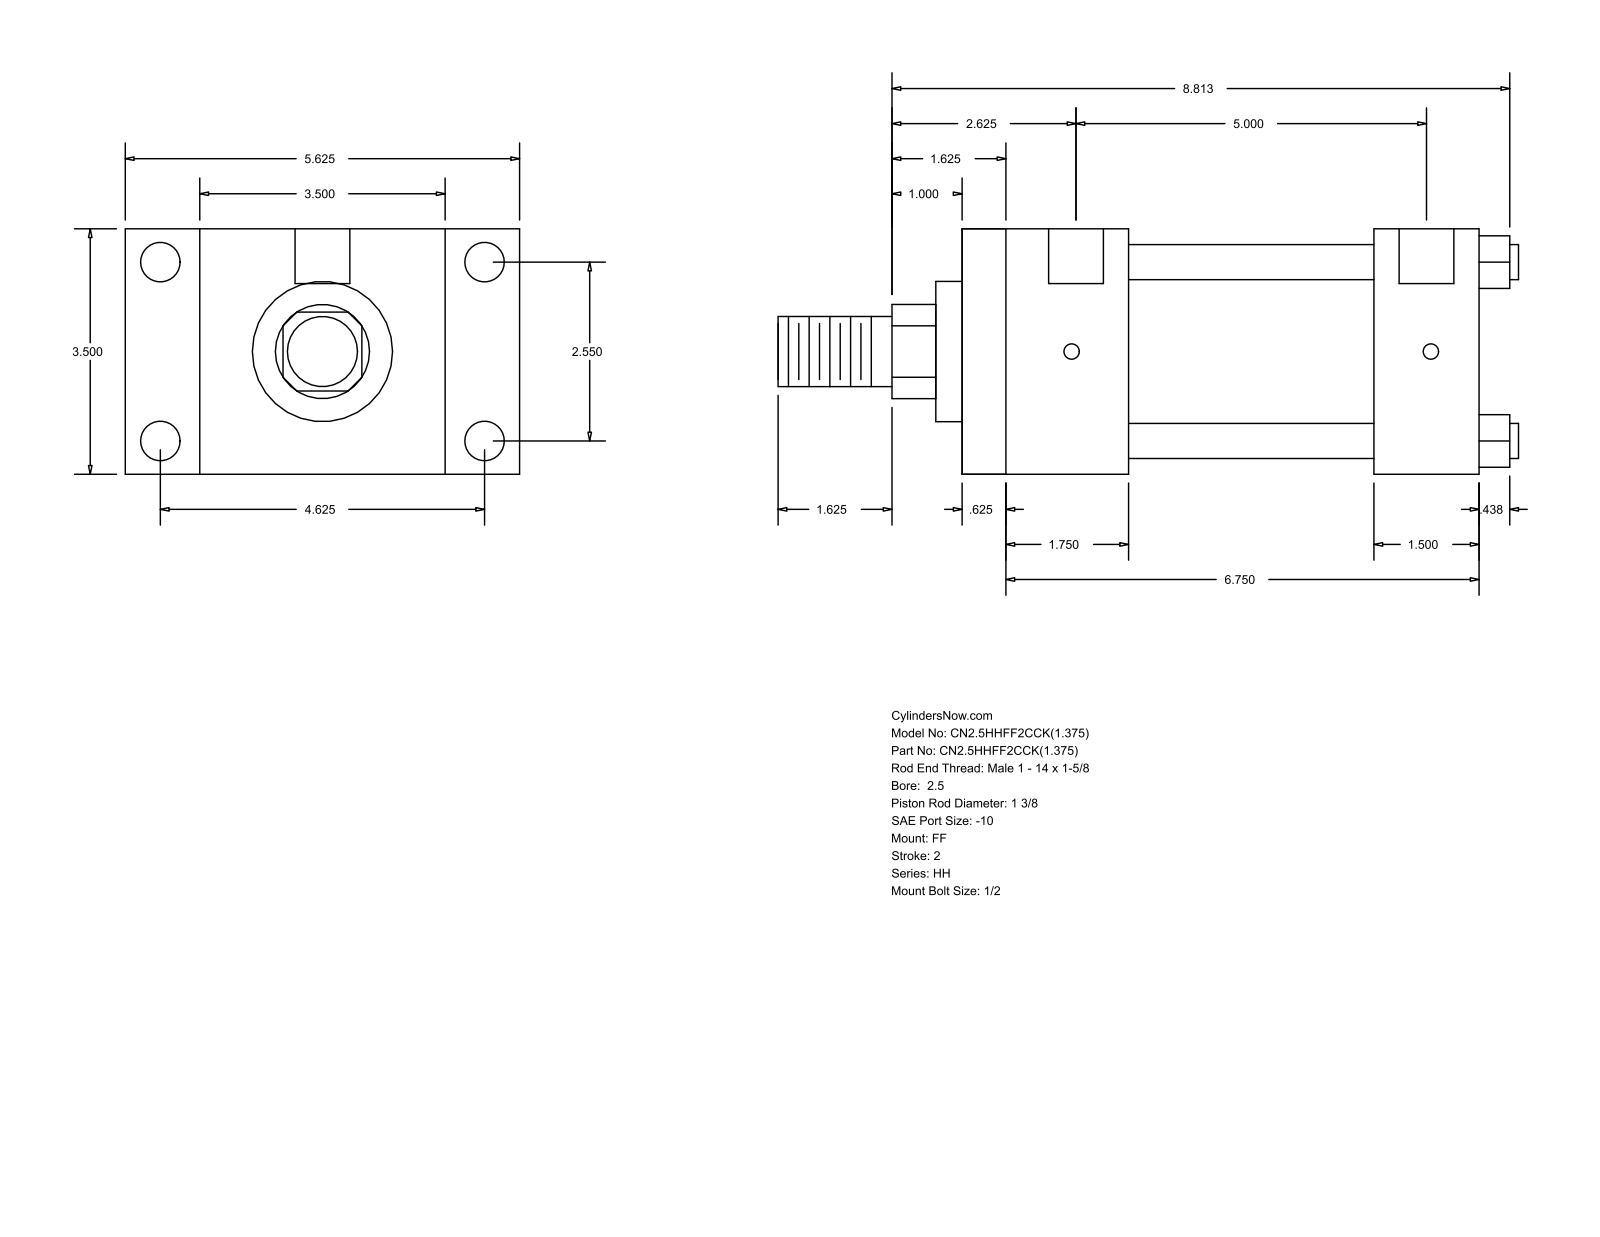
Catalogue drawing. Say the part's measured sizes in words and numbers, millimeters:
The part is named "HH_FF__0250_1.375". Its 3-D file was written by "GSSL Pune (CONFIG_CONTROL_DESIGN)". It is 0 solids with 92 faces: 64 planar, 28 cylindrical and 0 other. Overall it measures 268.29 by 142.88 by 88.9 millimeters. Round holes: 4 of diameter 5.56, 4 of diameter 14.3, 2 of diameter 19.84. Round bosses or shafts: 4 of diameter 12.7, 1 of diameter 73.03, 1 of diameter 50.8, 1 of diameter 34.92, 1 of diameter 25.4. Partial cylindrical surfaces (rounded edges, fillets, slot ends): 1 of radius 17.06. The main face-to-face distances are 88.9, 187.32, 15.87, 171.45, 60.32, 44.45, 127, 149.22, 133.35, 38.1. The hole center spacings are 1.58, 64.76, 117.48, 128.59, 130.17, 134.15, 127.01.
